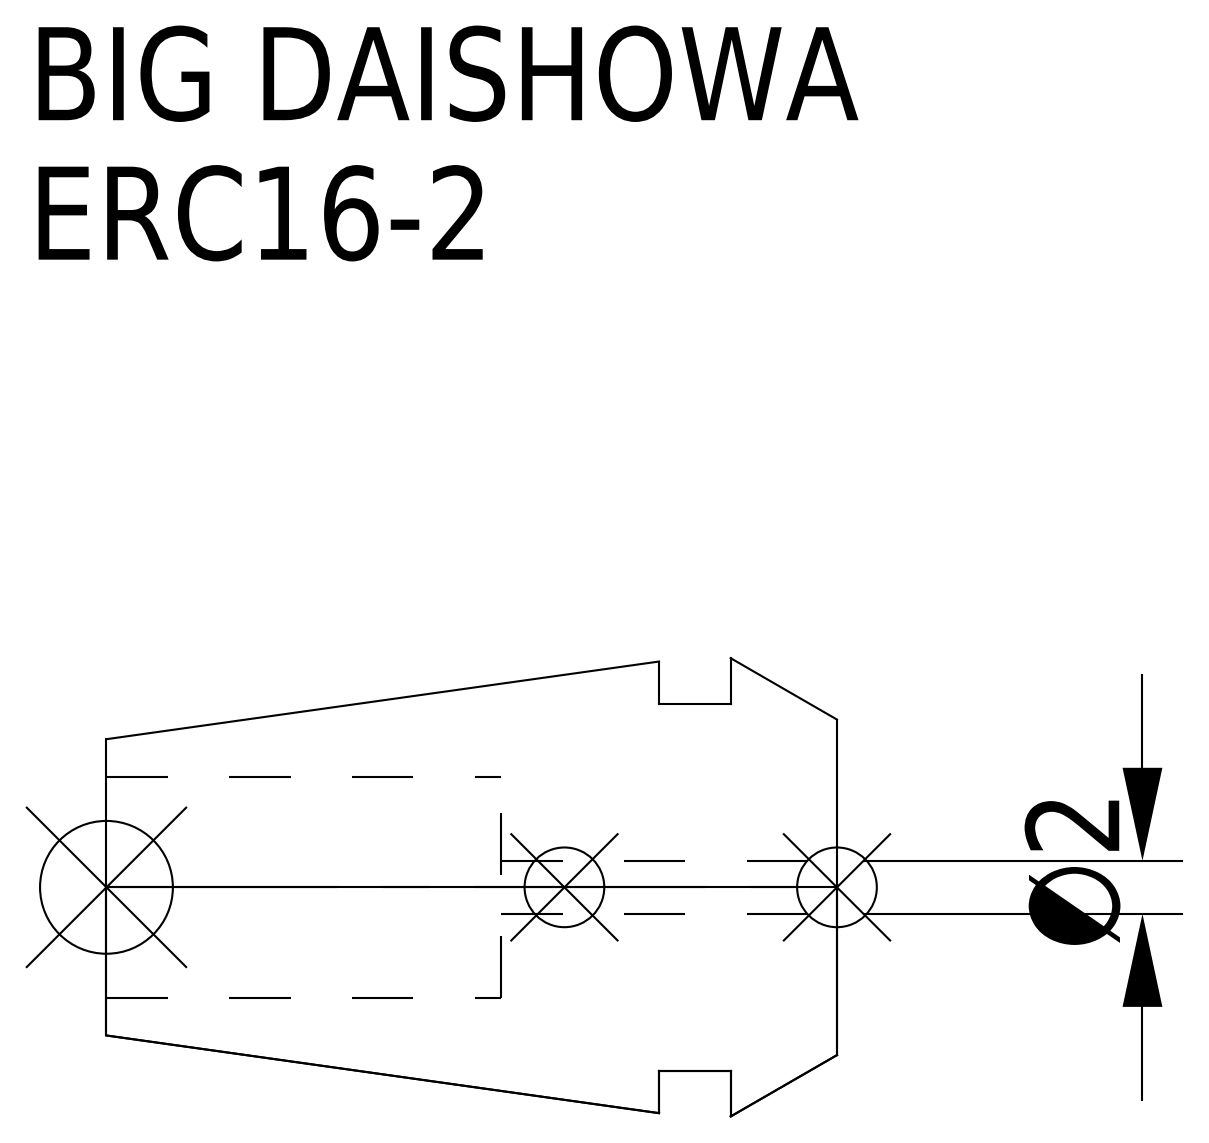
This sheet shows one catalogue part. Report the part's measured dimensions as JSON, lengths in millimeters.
{"part_name": "ERC16-2", "step_written_by": "CREO PARAMETRIC BY PTC INC, 2016380 (AUTOMOTIVE_DESIGN)", "units": "millimeters", "bodies": {"solids": 1, "faces": 15, "planar": 5, "cylindrical": 6, "other": 4}, "overall_size": [27.5, 17.25, 17.25], "volume_mm3": 3551, "surface_area_mm2": 2108, "round_holes": [[2, 1], [8.3, 1]], "round_bosses_or_shafts": [[13.8, 1]], "face_to_face_distances": [4, 6.7, 2.7, 12.63, 8.63, 5.93, 27.5, 23.5, 20.8, 14.87]}
